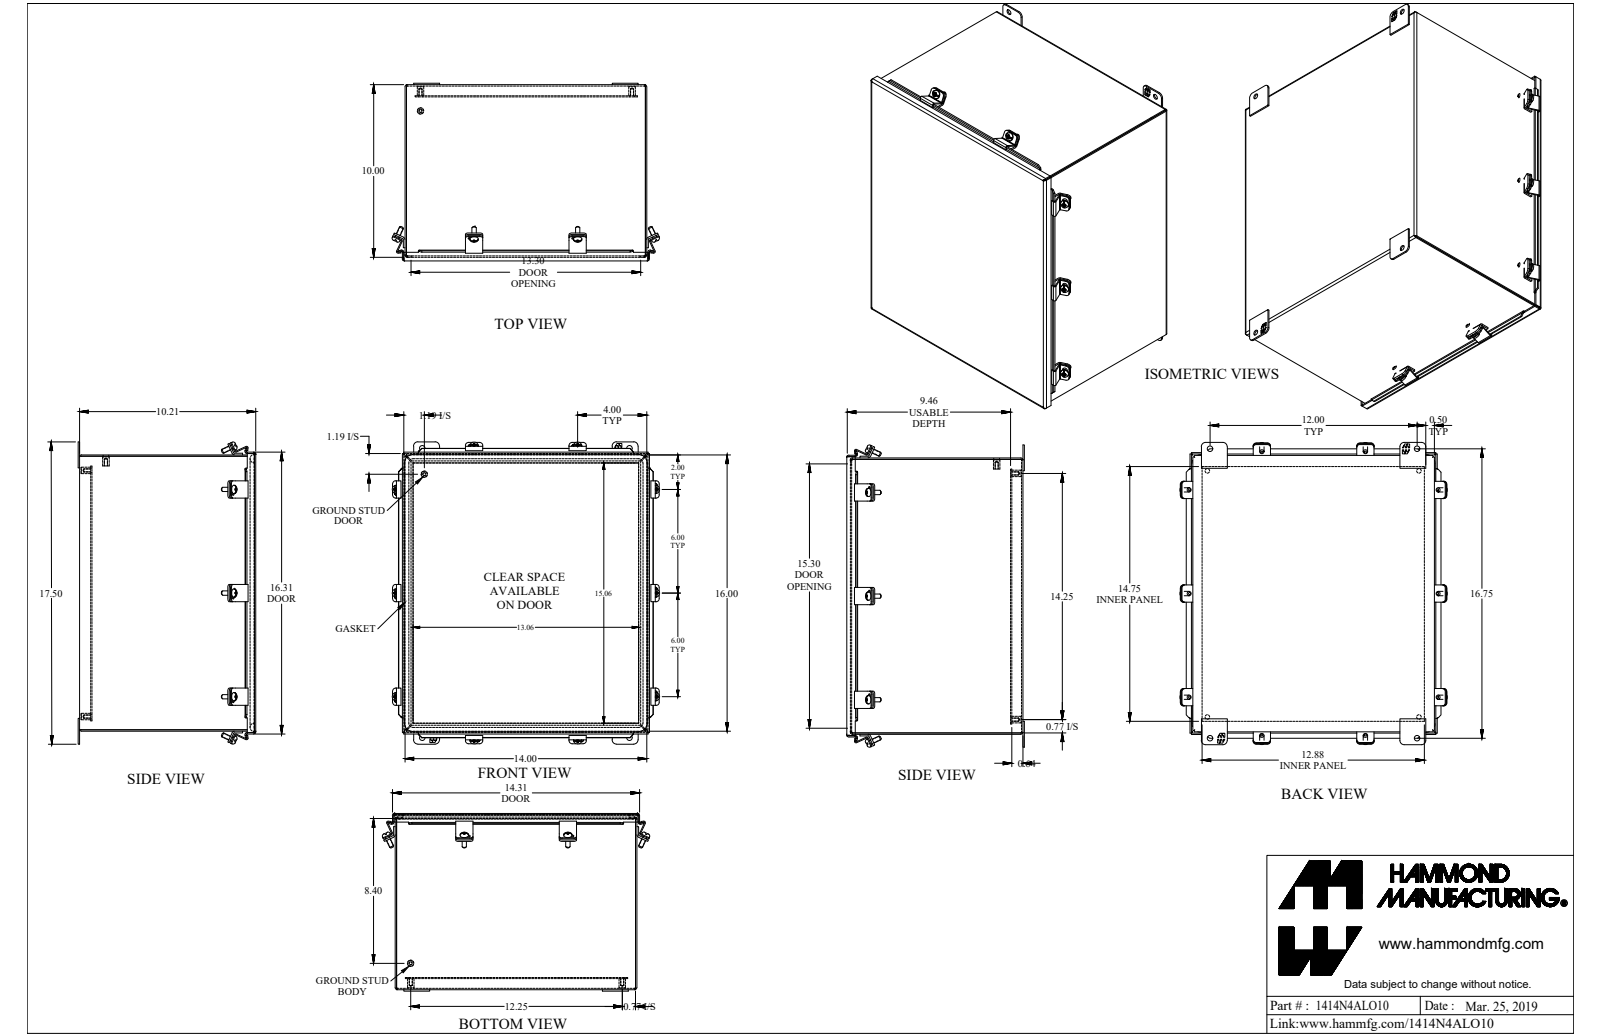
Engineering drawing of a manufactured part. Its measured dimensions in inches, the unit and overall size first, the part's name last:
Units: inches
Overall size (bounding box): 17.5 × 15.49 × 10.286
Round holes (diameter × count): ⌀0.213 ×10, ⌀0.159 ×6, ⌀0.265 ×4, ⌀0.313 ×4
Round bosses / shafts (diameter × count): ⌀0.48 ×10, ⌀0.25 ×10, ⌀0.375 ×6, ⌀0.33 ×6
Partial cylindrical surfaces — rounded edges, fillets, slot ends (radius × count): R0.141 ×20, R0.188 ×20, R0.25 ×12, R0.01 ×8, R0.029 ×8, R0.036 ×8, R0.048 ×8, R0.086 ×8
Main face-to-face distances: 0.081, 10.125, 13.919, 15.919, 10.206, 10.044, 0.562, 0.643, 9.563, 9.482
Hole centre spacings: 6, 12, 12.25, 14.25, 16.75, 18.792, 20.605, 0.31
Volume: 111.6 in³ · Surface area: 2 824 in²
Bodies: 44 solids, 1213 faces (829 planar, 276 cylindrical, 108 other)
Part name (STEP PRODUCT): 1414N4ALO10
STEP written by: SolidWorks 2018 (AUTOMOTIVE_DESIGN)
